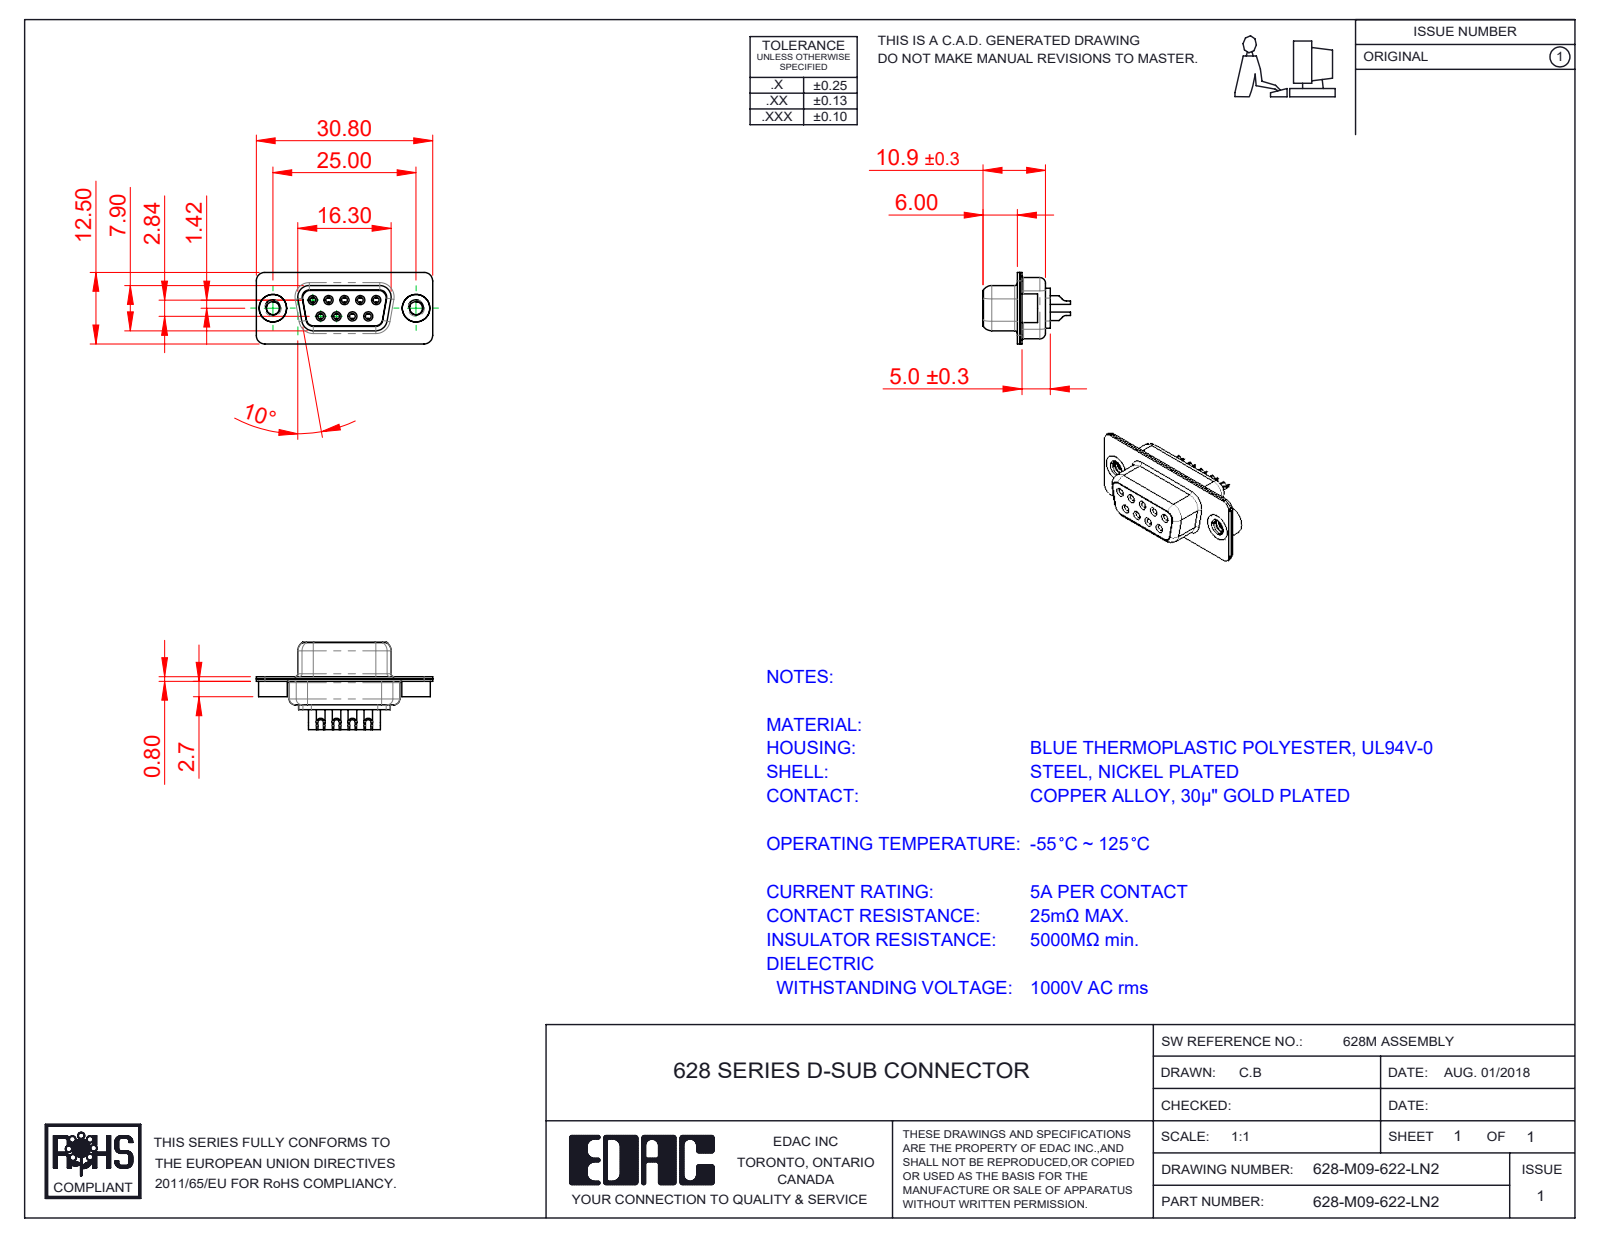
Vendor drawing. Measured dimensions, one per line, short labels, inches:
name: 628M Shell Front_09 Contacts; 628M Housing_09 Contacts; 628M Contact Row 1_22; 628M Shell Rear_09 Contacts (+3 more)
written by: SolidWorks 2020 (CONFIG_CONTROL_DESIGN)
unit: in
bodies: 14 solids, 775 faces (221 planar, 326 cylindrical, 228 other)
size: 1.213 × 0.6 × 0.492
volume: 0.105 in³; area: 6.983 in²
holes: 9× ⌀0.039, 9× ⌀0.043, 9× ⌀0.067, 9× ⌀0.071, 9× ⌀0.079, 2× ⌀0.089, 2× ⌀0.157, 2× ⌀0.189
bosses: 9× ⌀0.087, 9× ⌀0.063, 9× ⌀0.059, 2× ⌀0.197, 2× ⌀0.193
rounds: 16× R0.059, 12× R0.079, 8× R0.053, 8× R0.063, 6× R0.039, 4× R0.01, 4× R0.02, 4× R0.024
face distances: 0.016, 0.055, 0.018, 0.333, 0.031, 0.35, 0.071, 0.039, 0.278, 0.033
hole spacings: 0.124, 0.109, 0.218, 0.198, 0.198, 0.327, 0.28, 0.294
